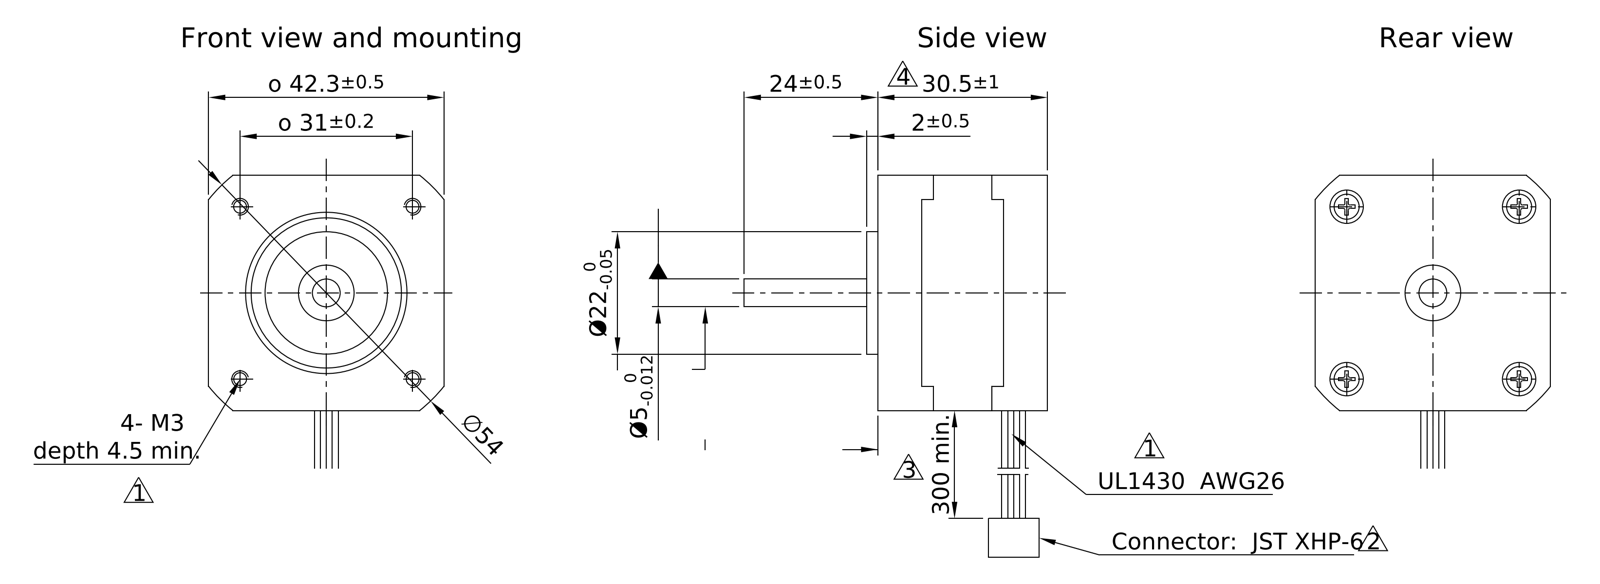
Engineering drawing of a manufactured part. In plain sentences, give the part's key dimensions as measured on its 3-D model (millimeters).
The part is named "ST4118S..._A". Its 3-D file was written by "Autodesk Inventor 2017 (AUTOMOTIVE_DESIGN)". It is 9 solids with 255 faces: 131 planar, 48 cylindrical and 76 other. Overall it measures 54.54 by 54.15 by 42.3 millimeters. Its volume is 53 308 cubic millimeters and its surface area 17 531 square millimeters. Round holes: 4 of diameter 1, 4 of diameter 2.46, 4 of diameter 2.7, 4 of diameter 6, 1 of diameter 5, 1 of diameter 7.5. Round bosses or shafts: 4 of diameter 2.5, 4 of diameter 2.27, 1 of diameter 22, 1 of diameter 1. Partial cylindrical surfaces (rounded edges, fillets, slot ends): 1 of radius 25, 1 of radius 27. The main face-to-face distances are 12.5, 9, 21.5, 42.15, 42, 30.5, 2, 42.3, 11, 19.5. The hole center spacings are 21.92, 31, 43.84, 1, 2, 3.
